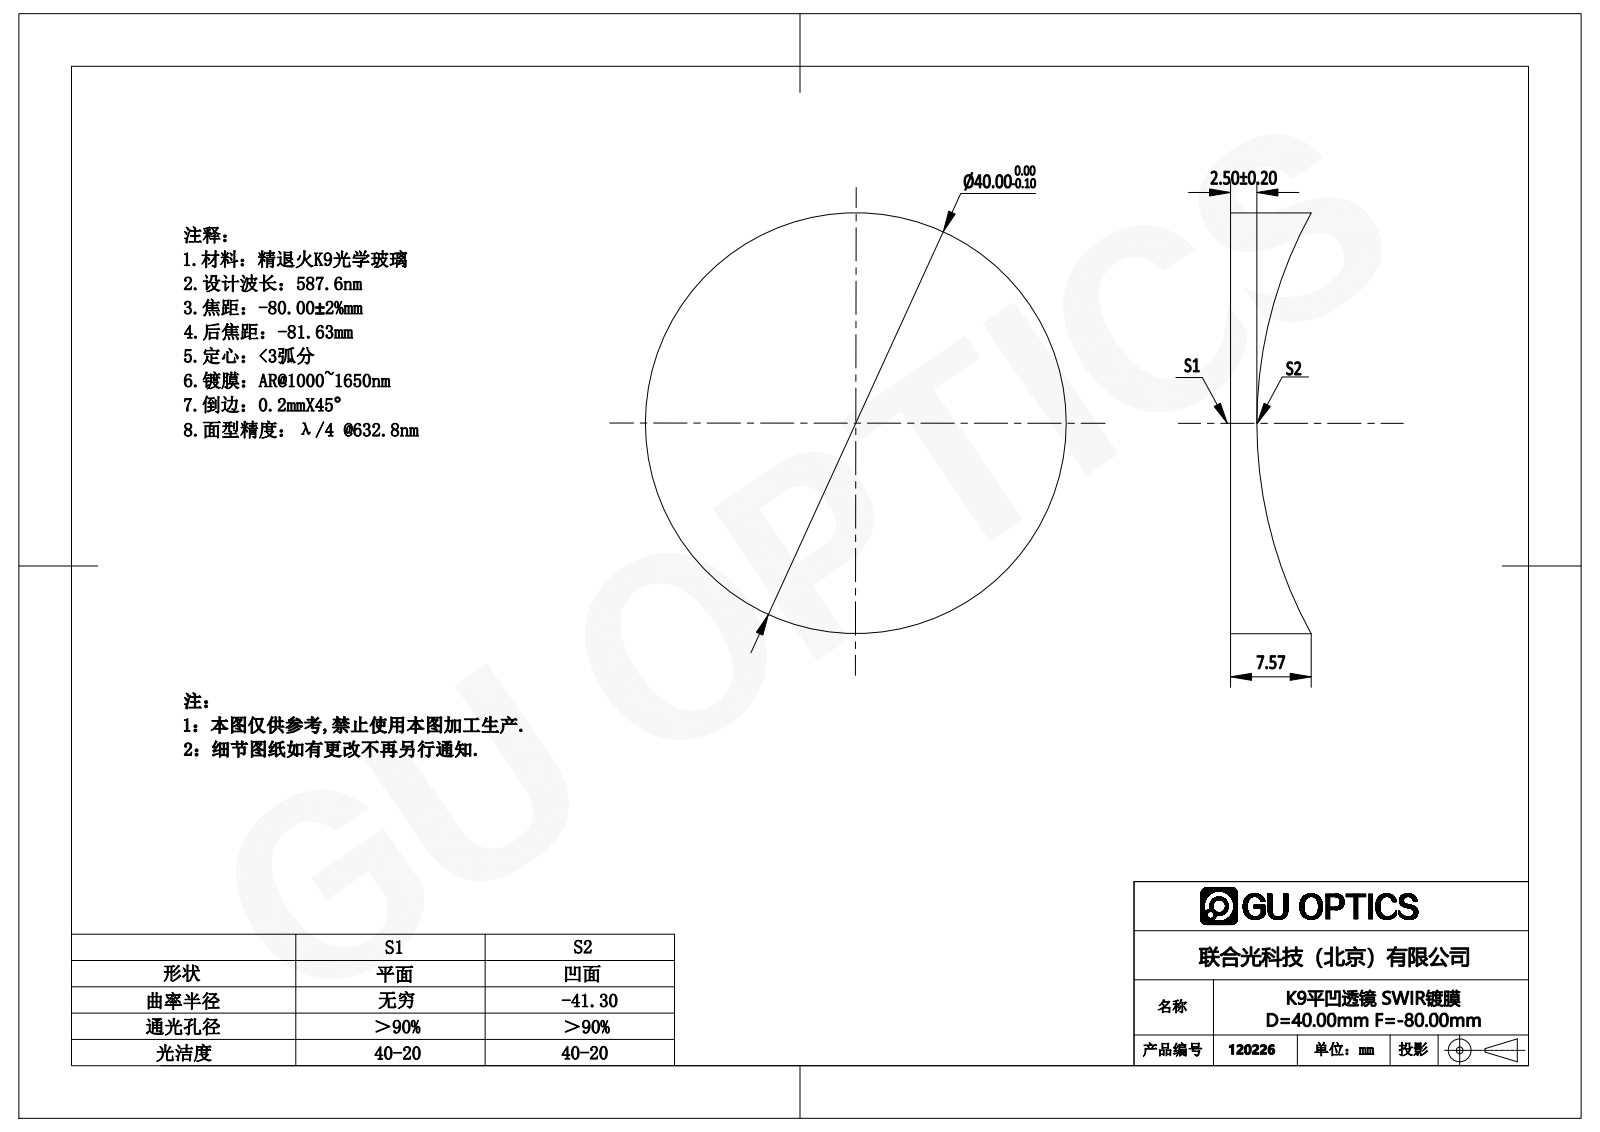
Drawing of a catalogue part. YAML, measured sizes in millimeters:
part_name: "120166"
step_written_by: "SolidWorks 2016 (AUTOMOTIVE_DESIGN)"
units: millimeters
bodies: {solids: 1, faces: 5, planar: 1, cylindrical: 2, other: 2}
overall_size: [40, 40, 7.67]
volume: 6315
surface_area: 3560
round_bosses_or_shafts:
  - {diameter: 40, count: 1}
